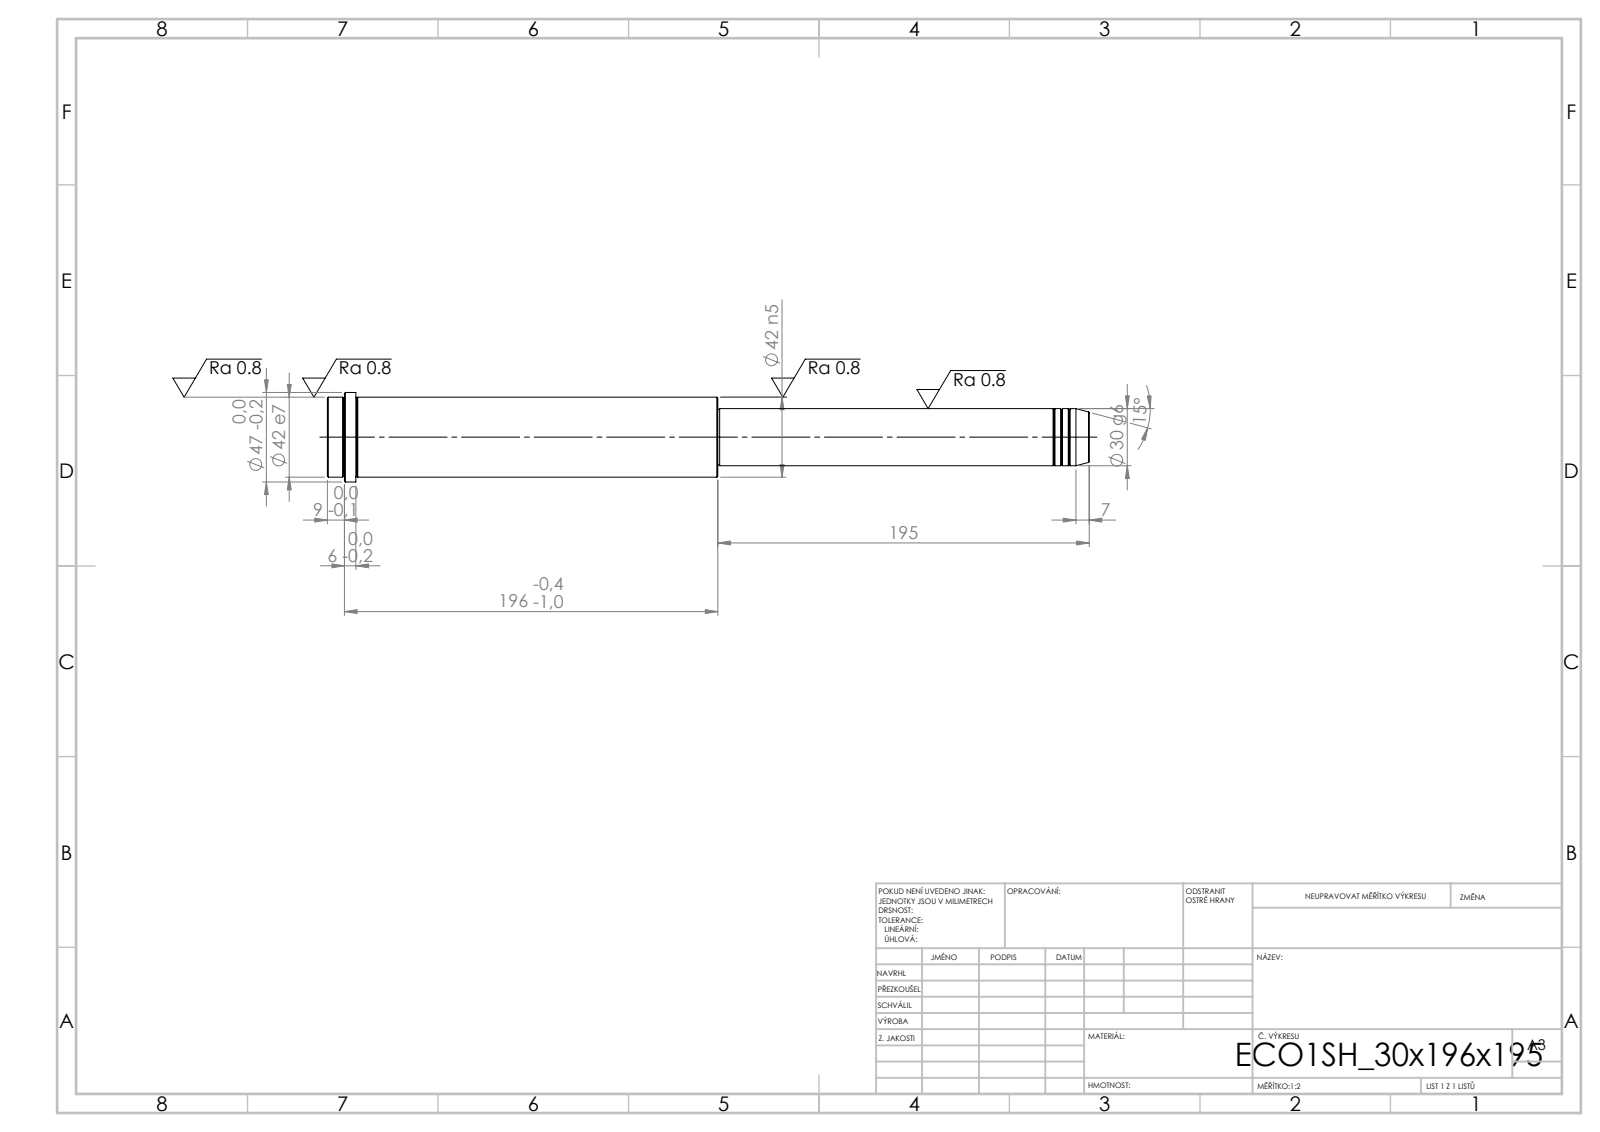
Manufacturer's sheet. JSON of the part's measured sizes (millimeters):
{"step_written_by": "SolidWorks 2019 (CONFIG_CONTROL_DESIGN)", "units": "millimeters", "bodies": {"solids": 1, "faces": 52, "planar": 6, "cylindrical": 16, "other": 30}, "overall_size": [400, 47, 47], "volume_mm3": 423045, "surface_area_mm2": 49061, "round_bosses_or_shafts": [[47, 1], [42, 1], [30, 1], [29, 1]], "face_to_face_distances": [205, 195, 400, 385, 190, 15, 391, 196, 6, 9]}
